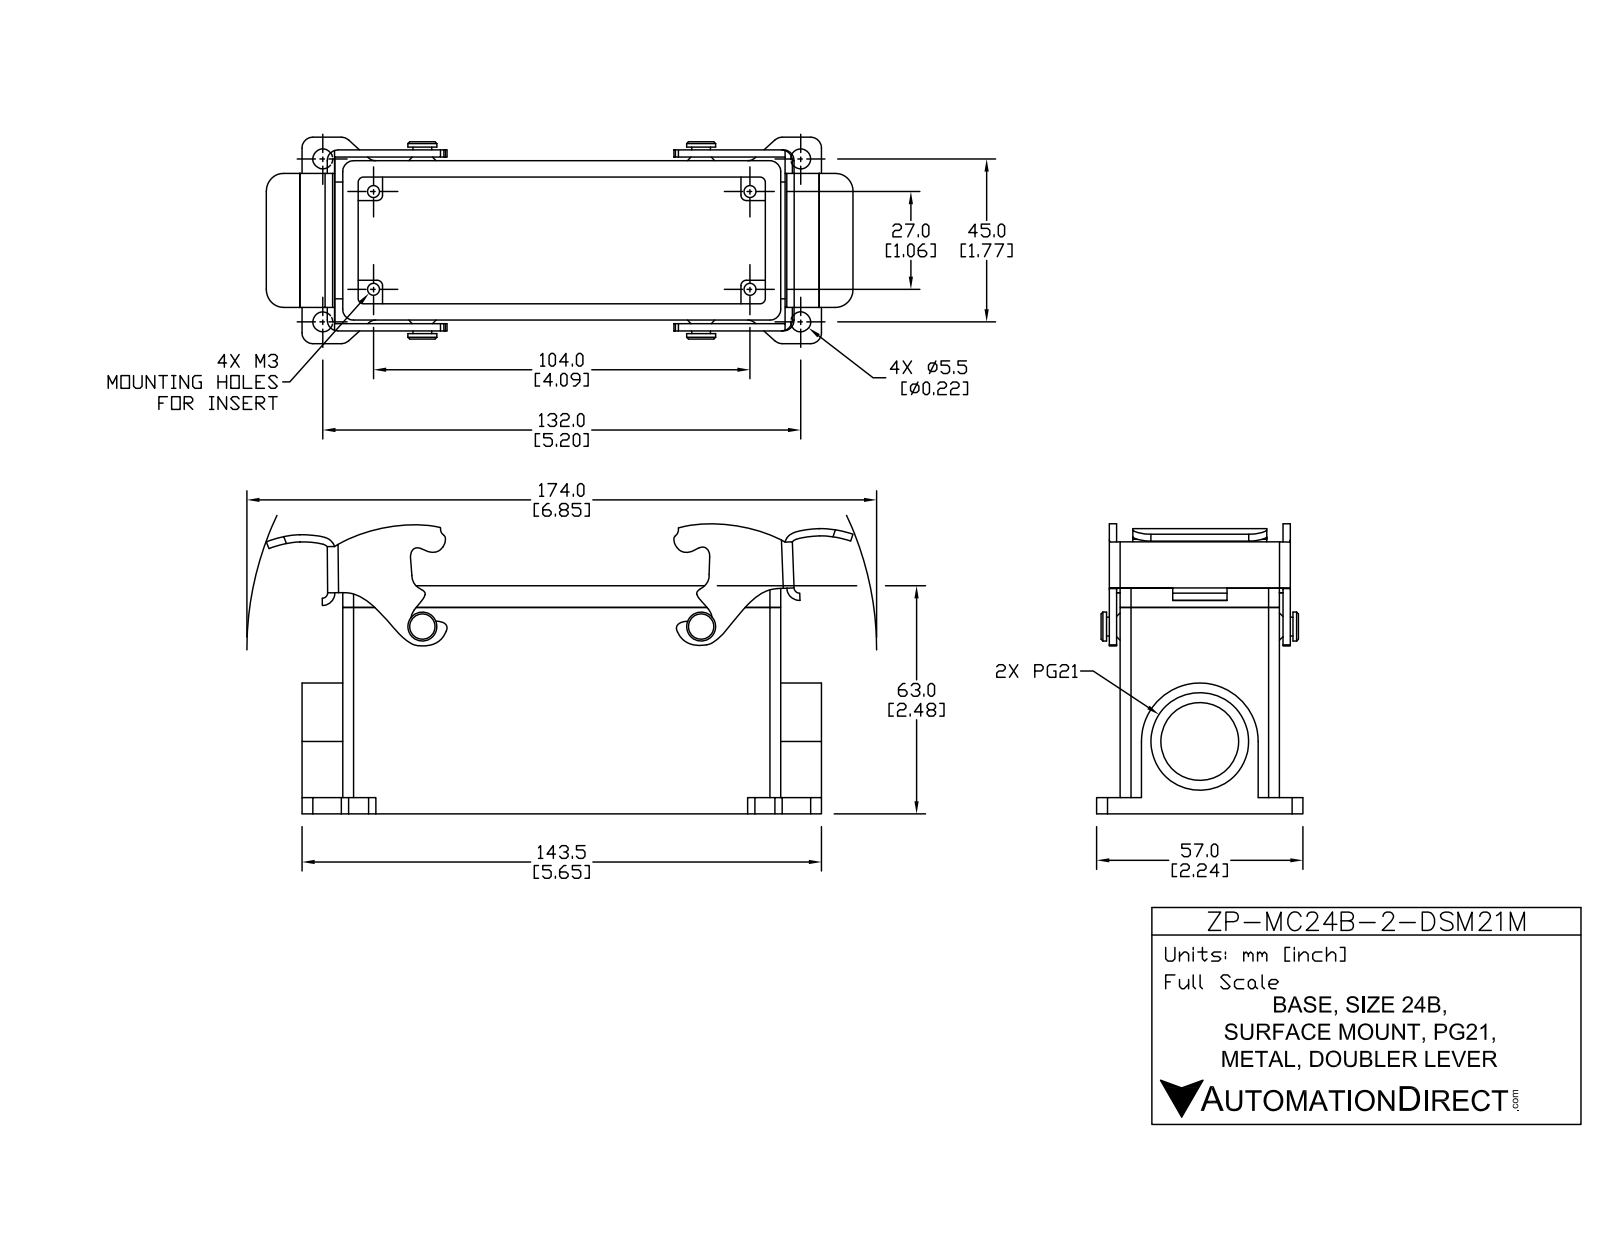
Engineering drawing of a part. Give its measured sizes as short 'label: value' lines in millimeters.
name: ZP-MC24B-2-DSM21M
written by: SolidWorks 2011 (AUTOMOTIVE_DESIGN)
unit: mm
bodies: 4 solids, 307 faces (125 planar, 174 cylindrical, 8 other)
size: 172.54 × 77.17 × 57
volume: 118 882 mm³; area: 69 318 mm²
holes: 4× ⌀3.3, 4× ⌀5.5, 1× ⌀21.5, 1× ⌀27
bosses: 2× ⌀8, 2× ⌀5.17
rounds: 26× R0.5, 18× R3, 8× R1.5, 6× R2, 6× R4, 4× R1, 4× R10, 2× R0.92
face distances: 4.5, 39.5, 44, 35, 2, 1.15, 57, 55, 1.25, 2.4
hole spacings: 16.64, 38.63, 118.34, 123.37, 27, 45, 104, 107.45
